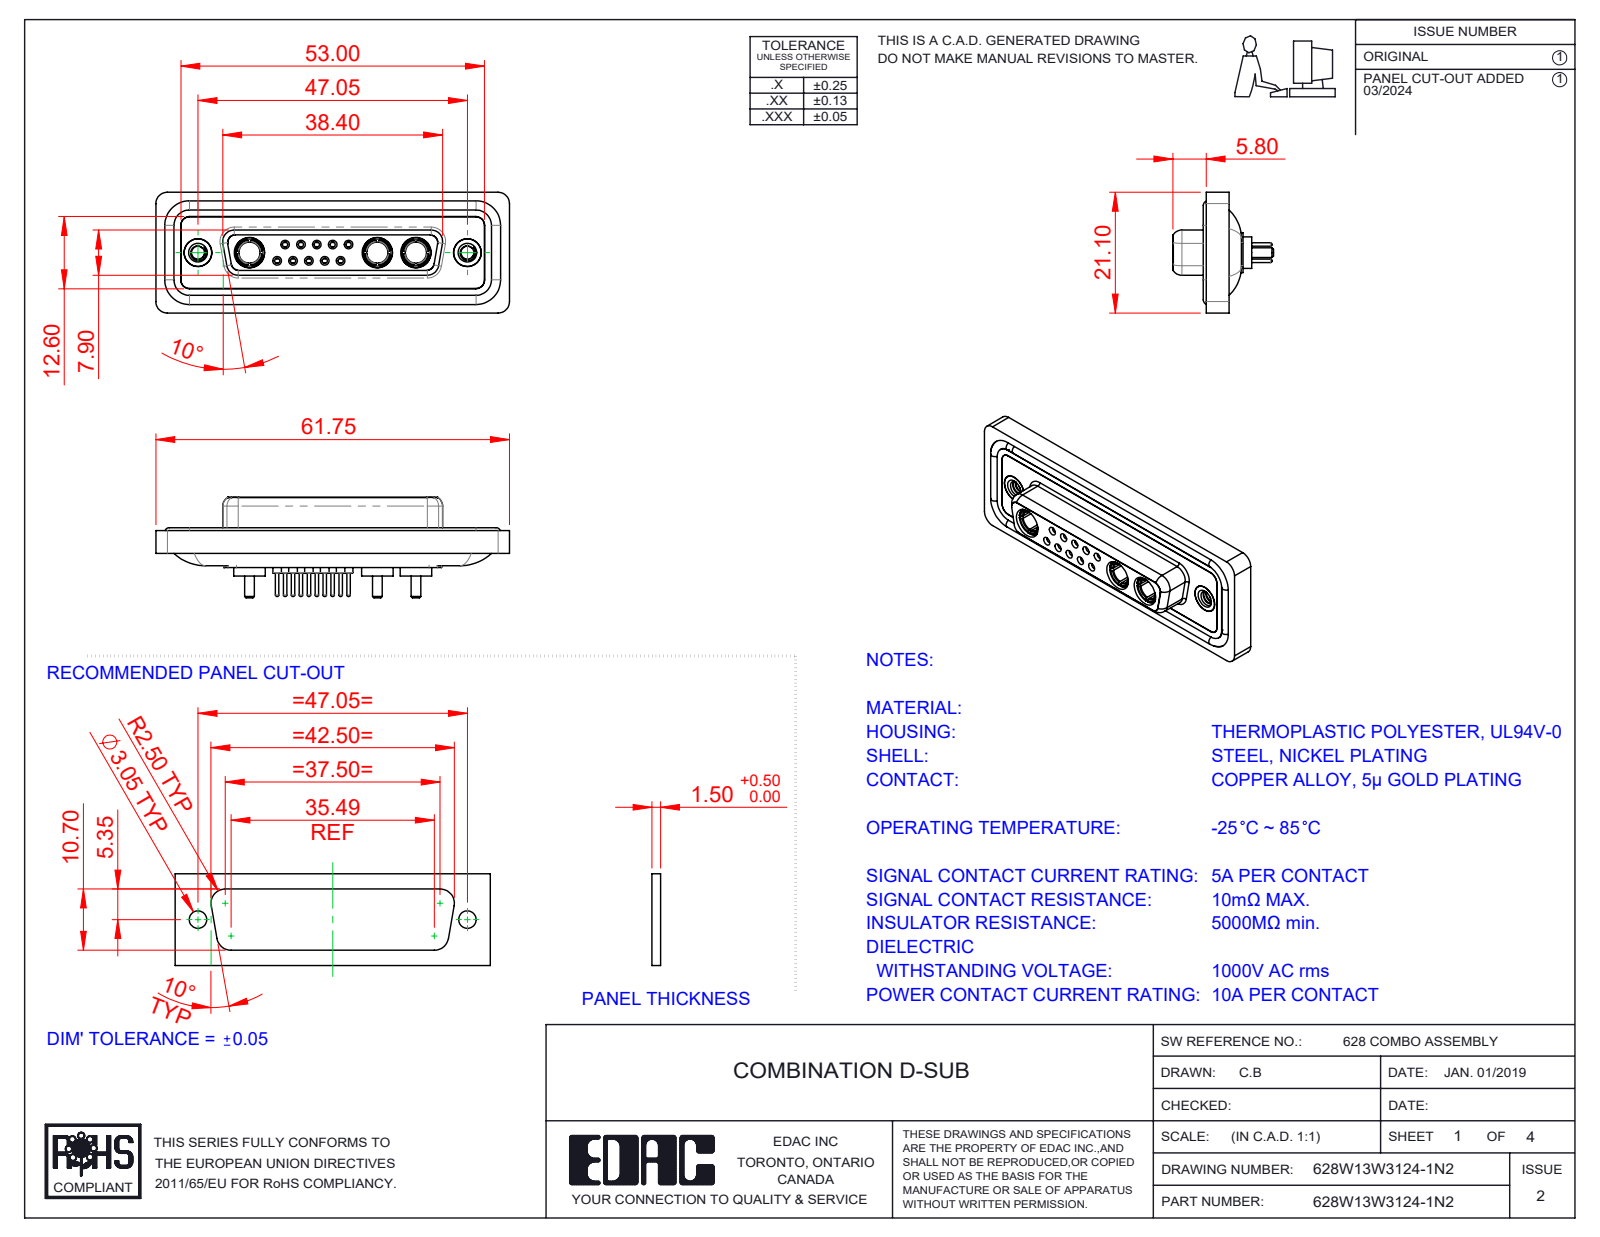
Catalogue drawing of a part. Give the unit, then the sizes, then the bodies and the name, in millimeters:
Units: millimetres
Overall size (bounding box): 61.75 × 21.1 × 17.55
Round holes (diameter × count): ⌀0.9 ×10, ⌀1.1 ×10, ⌀1.5 ×10, ⌀2 ×10, ⌀1.6 ×5, ⌀1.7 ×5, ⌀4.85 ×5, ⌀3.7 ×3, ⌀5.3 ×3, ⌀2.26 ×2, ⌀4 ×2, ⌀4.05 ×2
Round bosses / shafts (diameter × count): ⌀2.2 ×10, ⌀0.6 ×10, ⌀1.6 ×9, ⌀5.5 ×3, ⌀5.2 ×3, ⌀4.96 ×3, ⌀4.75 ×3, ⌀3.75 ×3
Partial cylindrical surfaces — rounded edges, fillets, slot ends (radius × count): R1.5 ×22, R2 ×18, R1.35 ×8, R1.6 ×8, R0.25 ×4, R0.5 ×4, R0.6 ×4, R0.65 ×4
Main face-to-face distances: 0.4, 1.8, 7.45, 5.65, 0.5, 6.6, 7.05, 1.6, 2.9, 1.1
Hole centre spacings: 3.16, 2.77, 5.03, 5.04, 5.54, 8.31, 7.49, 2.76
Volume: 8 229 mm³ · Surface area: 13 671 mm²
Bodies: 23 solids, 1158 faces (342 planar, 447 cylindrical, 369 other)
Part name (STEP PRODUCT): 628W13W3124-1N2; Power Socket_10A S; 628Combo Shell Rear_25 Contacts; 628Combo Threaded Rivet_2 (+5 more)
STEP written by: SolidWorks 2023 (CONFIG_CONTROL_DESIGN)
